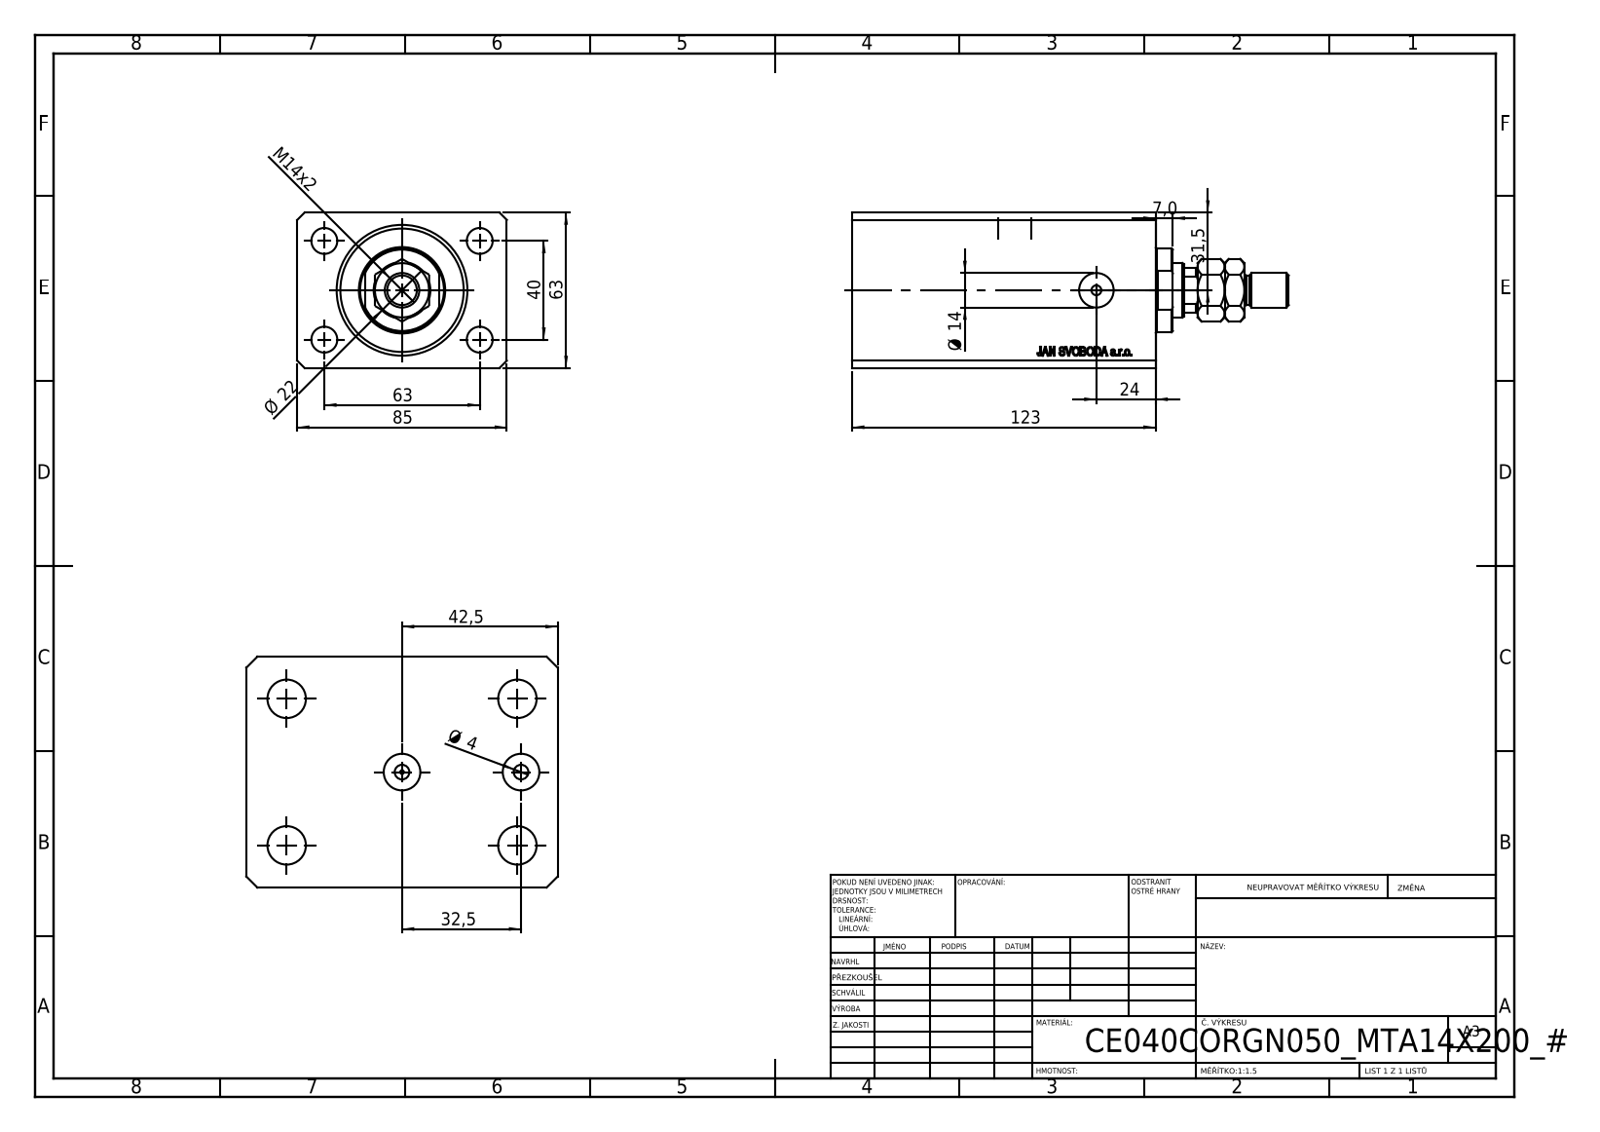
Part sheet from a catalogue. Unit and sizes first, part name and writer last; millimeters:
Units: millimetres
Overall size (bounding box): 177 × 85 × 63
Round holes (diameter × count): ⌀4 ×4, ⌀10.5 ×4, ⌀10 ×2, ⌀14 ×2, ⌀1.25 ×1, ⌀12.5 ×1, ⌀22 ×1, ⌀40 ×1, ⌀53 ×1
Round bosses / shafts (diameter × count): ⌀34 ×1, ⌀14 ×1, ⌀12 ×1
Partial cylindrical surfaces — rounded edges, fillets, slot ends (radius × count): R10.5 ×1
Main face-to-face distances: 63, 85, 123, 17, 106, 11.4, 94.6, 111.6, 100.4, 56
Hole centre spacings: 37.31, 20.02, 40, 63, 67.05, 74.63, 32.5, 75
Volume: 583 532 mm³ · Surface area: 105 663 mm²
Bodies: 4 solids, 917 faces (443 planar, 50 cylindrical, 424 other)
Part name (STEP PRODUCT): V250CE_C_Body; MTA; V250CE_C_VCP; V250CE_VC_C
STEP written by: SolidWorks 2019 (CONFIG_CONTROL_DESIGN)
